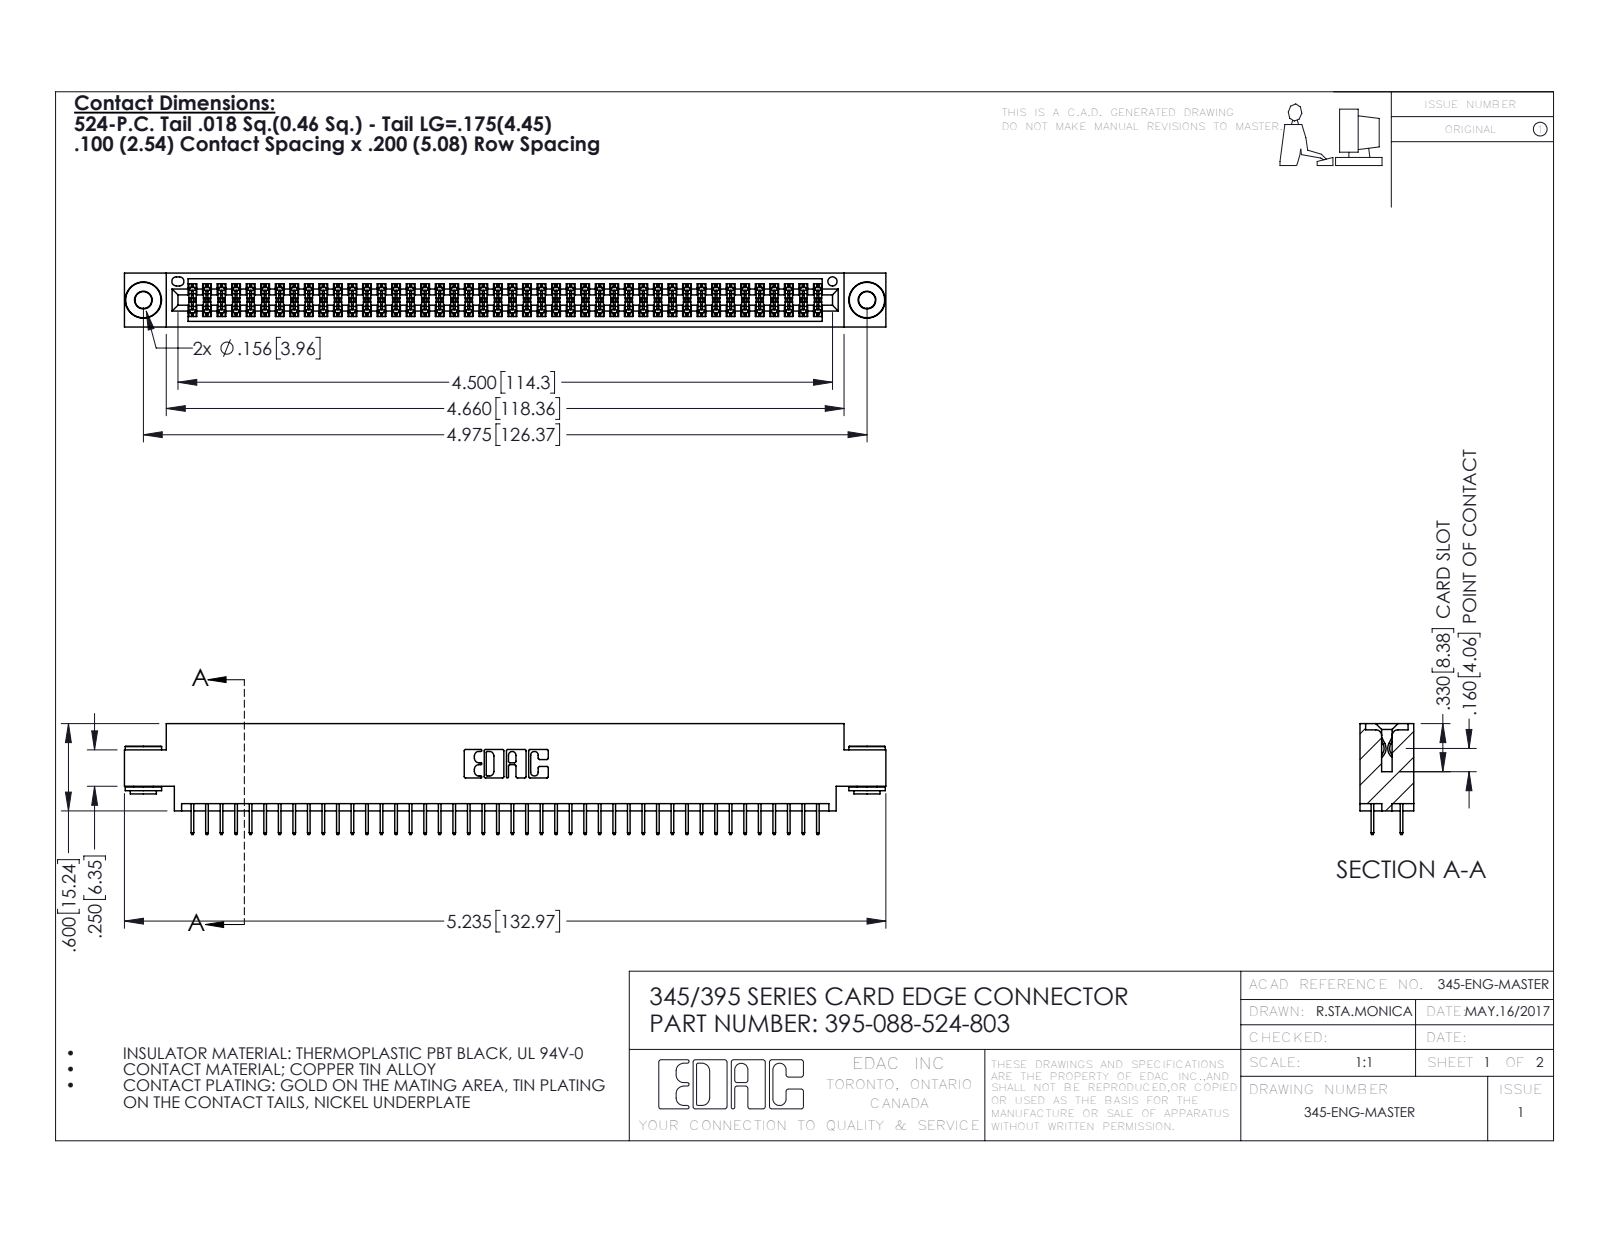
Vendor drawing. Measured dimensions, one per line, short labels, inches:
name: 395-088-524-803; 345 Part_0.170 Offset - 0.156 Dia-TH; 345-292-001_345-293-124; 345-250-002_345-250-002-102
written by: SolidWorks 2016 (CONFIG_CONTROL_DESIGN)
unit: in
bodies: 91 solids, 4920 faces (3526 planar, 1386 cylindrical, 8 other)
size: 5.235 × 0.762 × 0.37
volume: 0.775 in³; area: 29.17 in²
holes: 2× ⌀0.116, 2× ⌀0.156, 1× ⌀0.064
bosses: 2× ⌀0.25, 2× ⌀0.18, 2× ⌀0.136
rounds: 132× R0.006, 22× R0.01, 6× R0.007, 6× R0.031, 3× R0.026, 2× R0.014, 2× R0.019, 2× R0.022
face distances: 0.072, 0.298, 0.37, 0.2, 0.098, 0.272, 0.025, 0.225, 0.175, 0.072
hole spacings: 0.27, 4.739, 4.975
